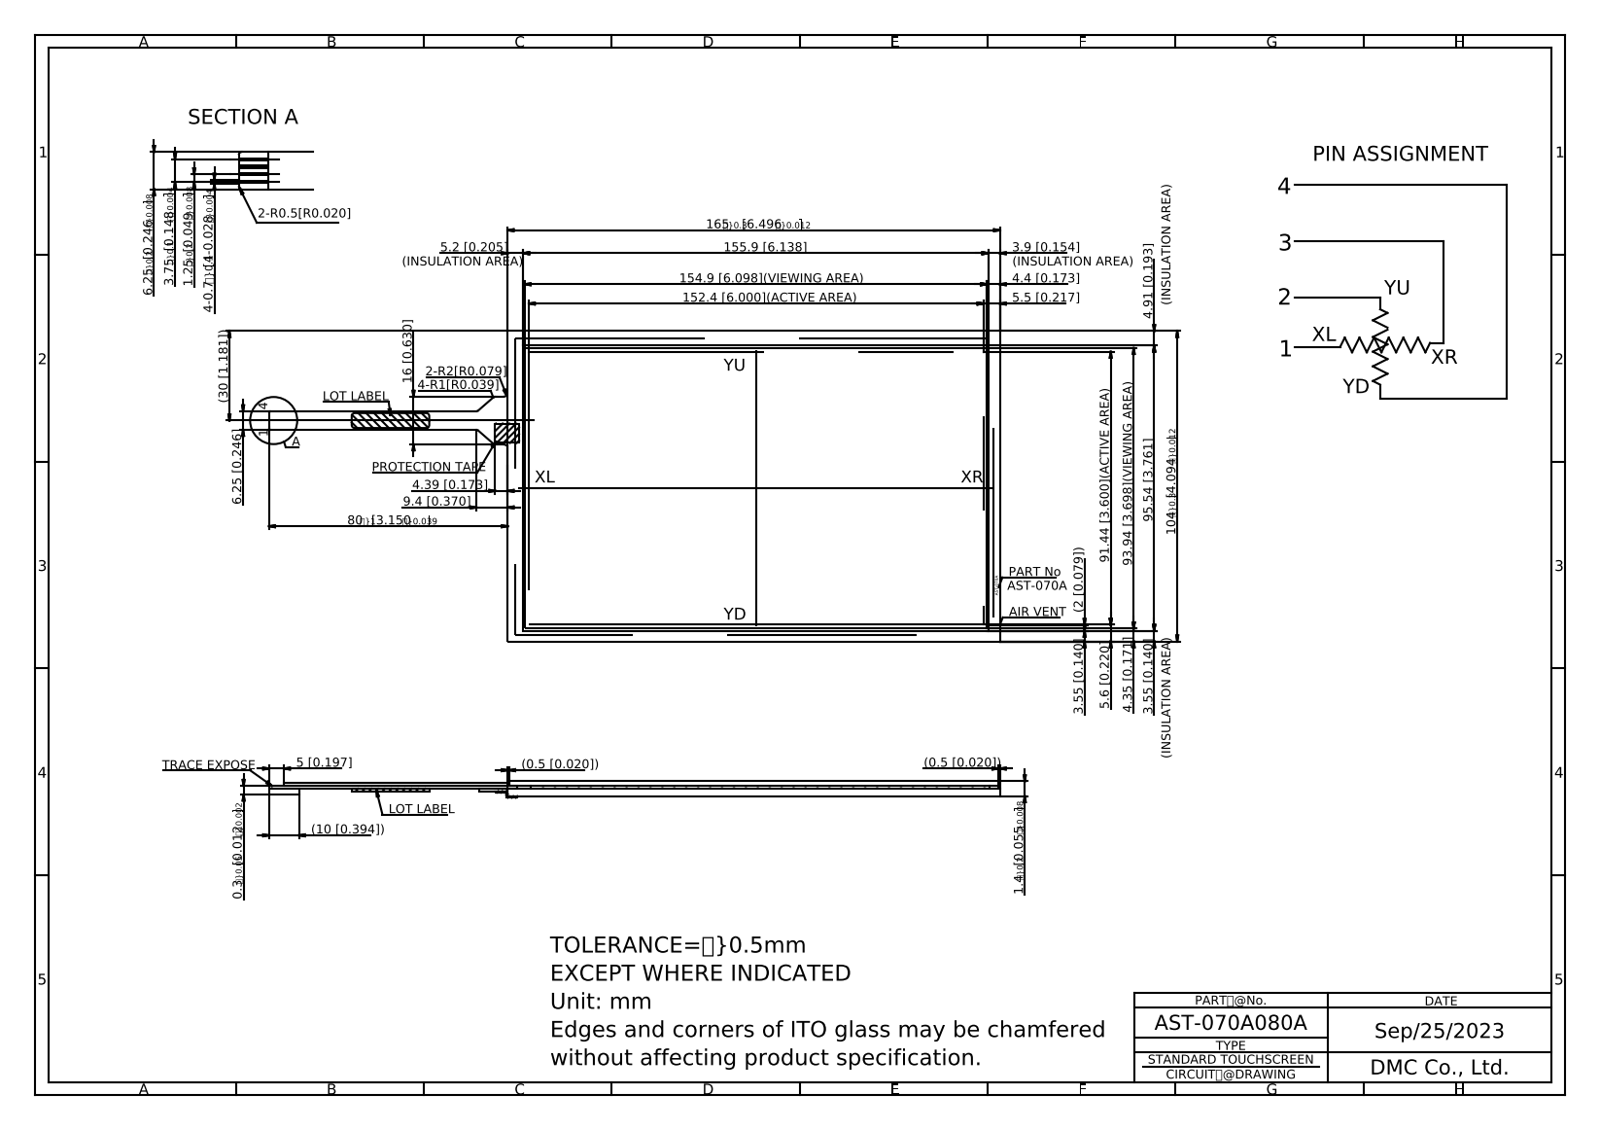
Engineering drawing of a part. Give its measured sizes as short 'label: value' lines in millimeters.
name: AST-070A080A
written by: Autodesk Inventor 2020 (CONFIG_CONTROL_DESIGN)
unit: mm
bodies: 1 solid, 51 faces (45 planar, 6 cylindrical, 0 other)
size: 278 × 145.6 × 1.4
volume: 24 034 mm³; area: 36 329 mm²
rounds: 4× R1, 2× R0.5
face distances: 1.4, 1.3, 1.2, 1.1, 104, 165, 0.8, 0.4, 0.5, 0.6
